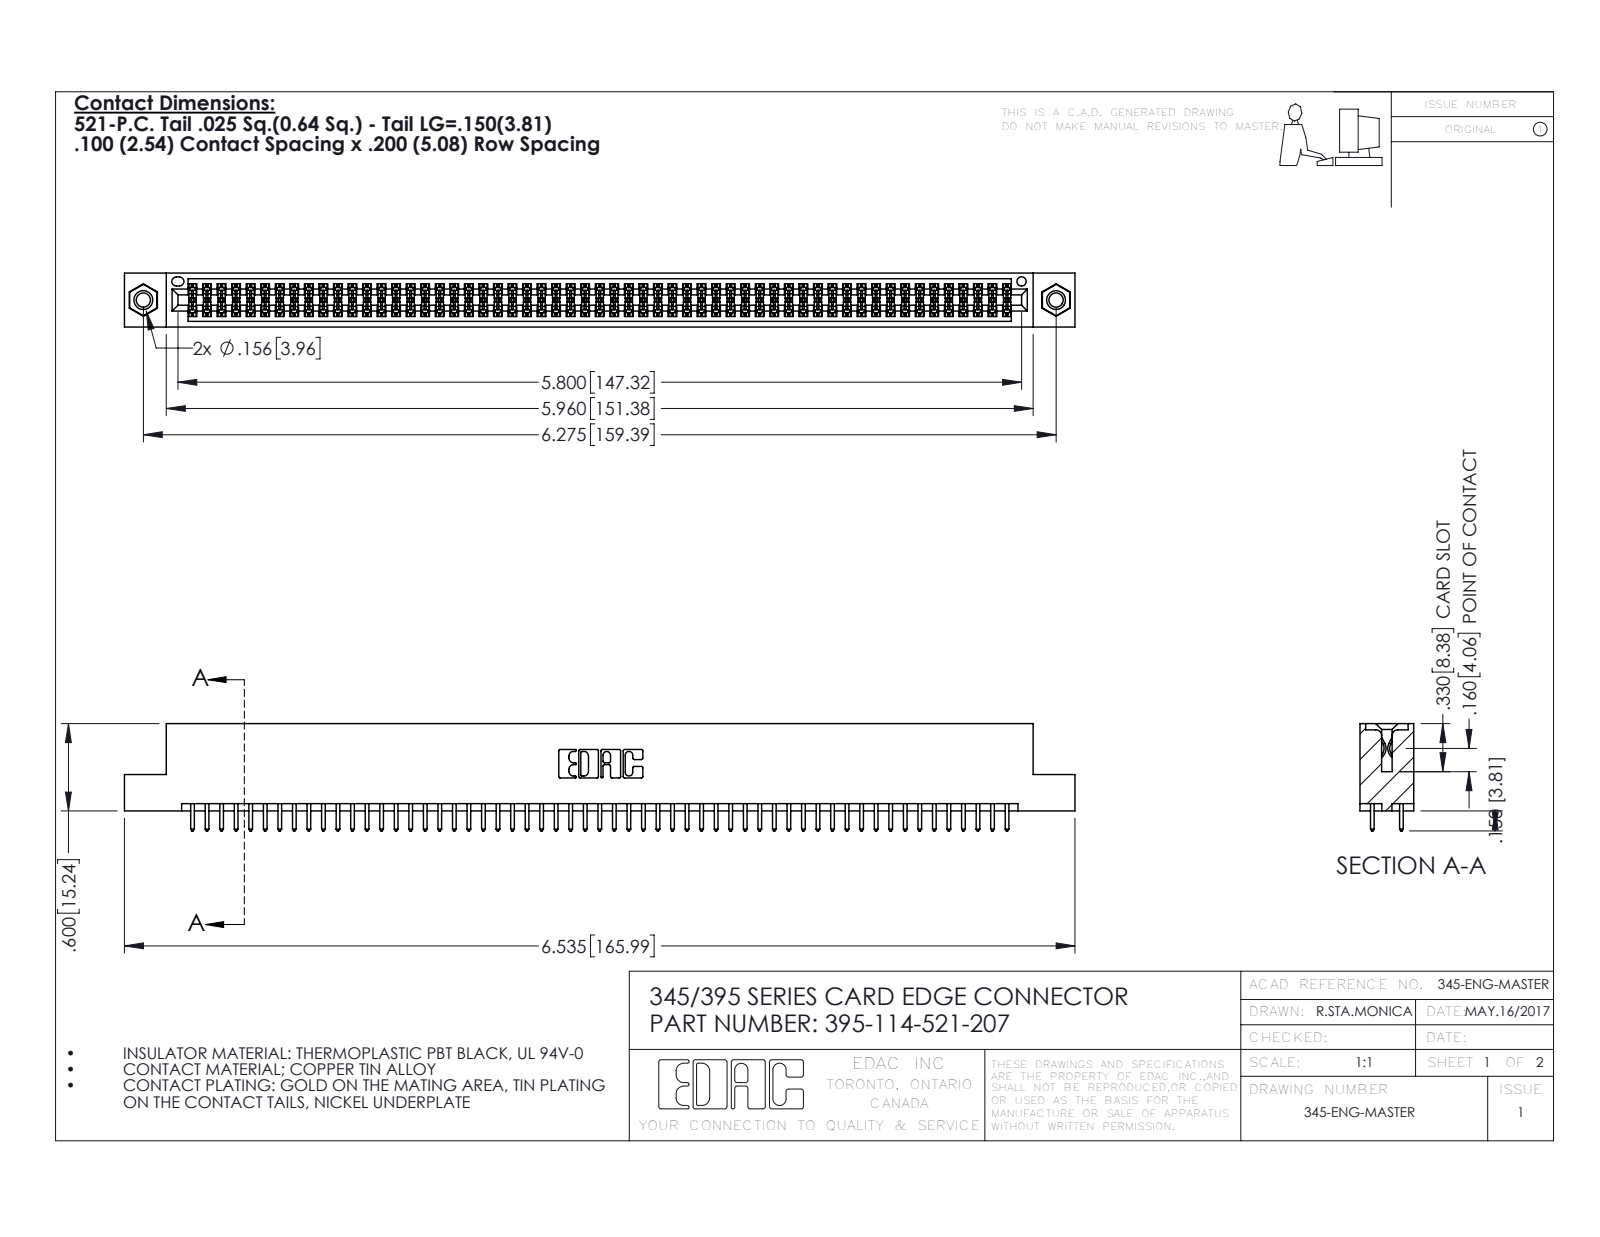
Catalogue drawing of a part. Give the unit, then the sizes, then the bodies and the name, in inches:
Units: inches
Overall size (bounding box): 6.535 × 0.737 × 0.37
Round holes (diameter × count): ⌀0.098 ×2, ⌀0.125 ×2, ⌀0.156 ×2, ⌀0.064 ×1
Round bosses / shafts (diameter × count): ⌀0.155 ×2
Partial cylindrical surfaces — rounded edges, fillets, slot ends (radius × count): R0.006 ×171, R0.01 ×114, R0.01 ×22, R0.007 ×6, R0.031 ×6, R0.026 ×3, R0.014 ×2, R0.019 ×2
Main face-to-face distances: 0.072, 0.298, 0.2, 0.098, 0.272, 0.025, 0.37, 0.225, 0.175, 0.149
Hole centre spacings: 0.27, 6.039, 6.275
Volume: 0.989 in³ · Surface area: 37.15 in²
Bodies: 117 solids, 5886 faces (3874 planar, 1996 cylindrical, 16 other)
Part name (STEP PRODUCT): 345-250-001_345-250-005-103; 395-114-521-207; 345 Part_Flush Mounting Lugs - 0.156 Dia-TI; 345-292-001_345-293-121
STEP written by: SolidWorks 2016 (CONFIG_CONTROL_DESIGN)
